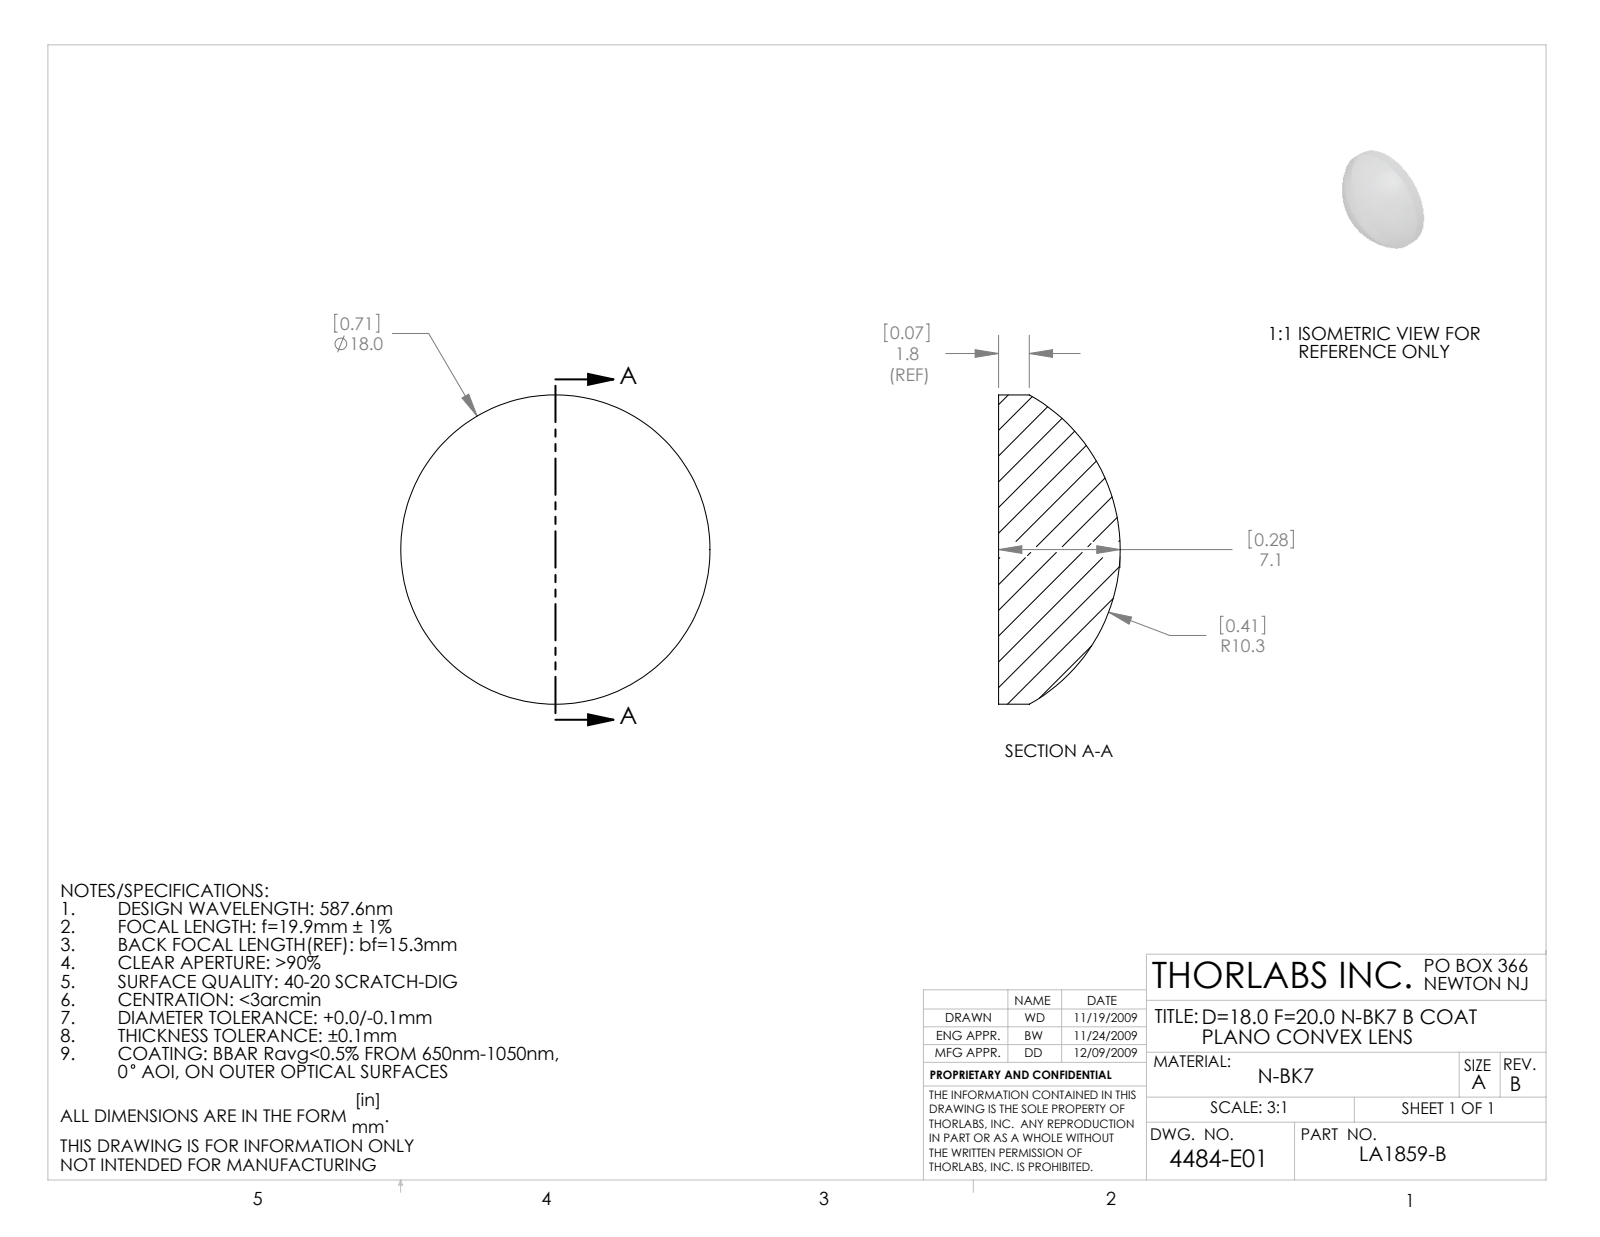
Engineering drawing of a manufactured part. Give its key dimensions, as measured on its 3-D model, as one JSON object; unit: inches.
{"part_name": "4484-E0W", "step_written_by": "SolidWorks 2009 (AUTOMOTIVE_DESIGN)", "units": "inches", "bodies": {"solids": 1, "faces": 5, "planar": 1, "cylindrical": 2, "other": 2}, "overall_size": [0.709, 0.709, 0.279], "volume_in3": 0.074, "surface_area_in2": 1.08, "round_bosses_or_shafts": [[0.709, 1]]}
